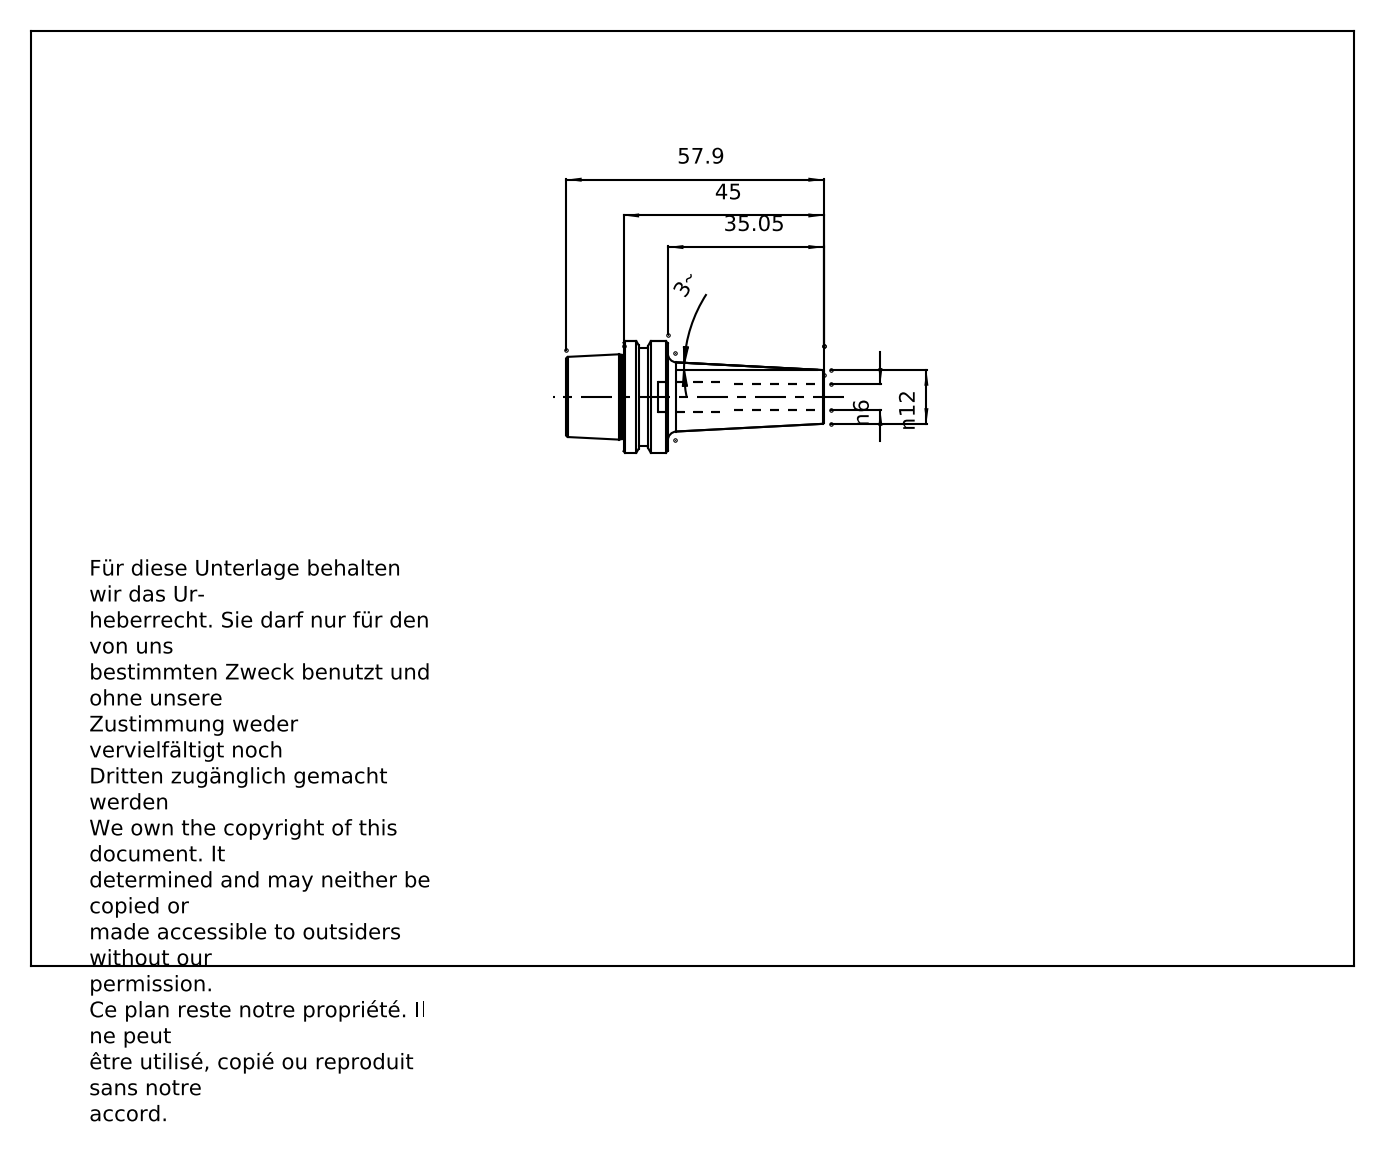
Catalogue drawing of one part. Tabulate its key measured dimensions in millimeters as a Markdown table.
| quantity | value |
| --- | --- |
| part name | E25-180-06 |
| STEP written by | PRO/ENGINEER BY PARAMETRIC TECHNOLOGY CORPORATION, 2010430 (CONFIG_CONTROL_DESIGN) |
| units | millimeters |
| bodies | 1 solid, 60 faces (8 planar, 16 cylindrical, 36 other) |
| overall size | 57.9 × 25 × 25 |
| volume | 9 081 mm³ |
| surface area | 5 641 mm² |
| round holes (diameter × count) | 6 × 1, 14.04 × 1, 16.45 × 1 |
| round bosses / shafts (diameter × count) | 25 × 1, 21.95 × 1, 18.96 × 1 |
| main face-to-face distances | 4, 5.95, 9.95, 45, 39.05, 35.05, 12.9, 18.85, 22.85, 57.9 |
